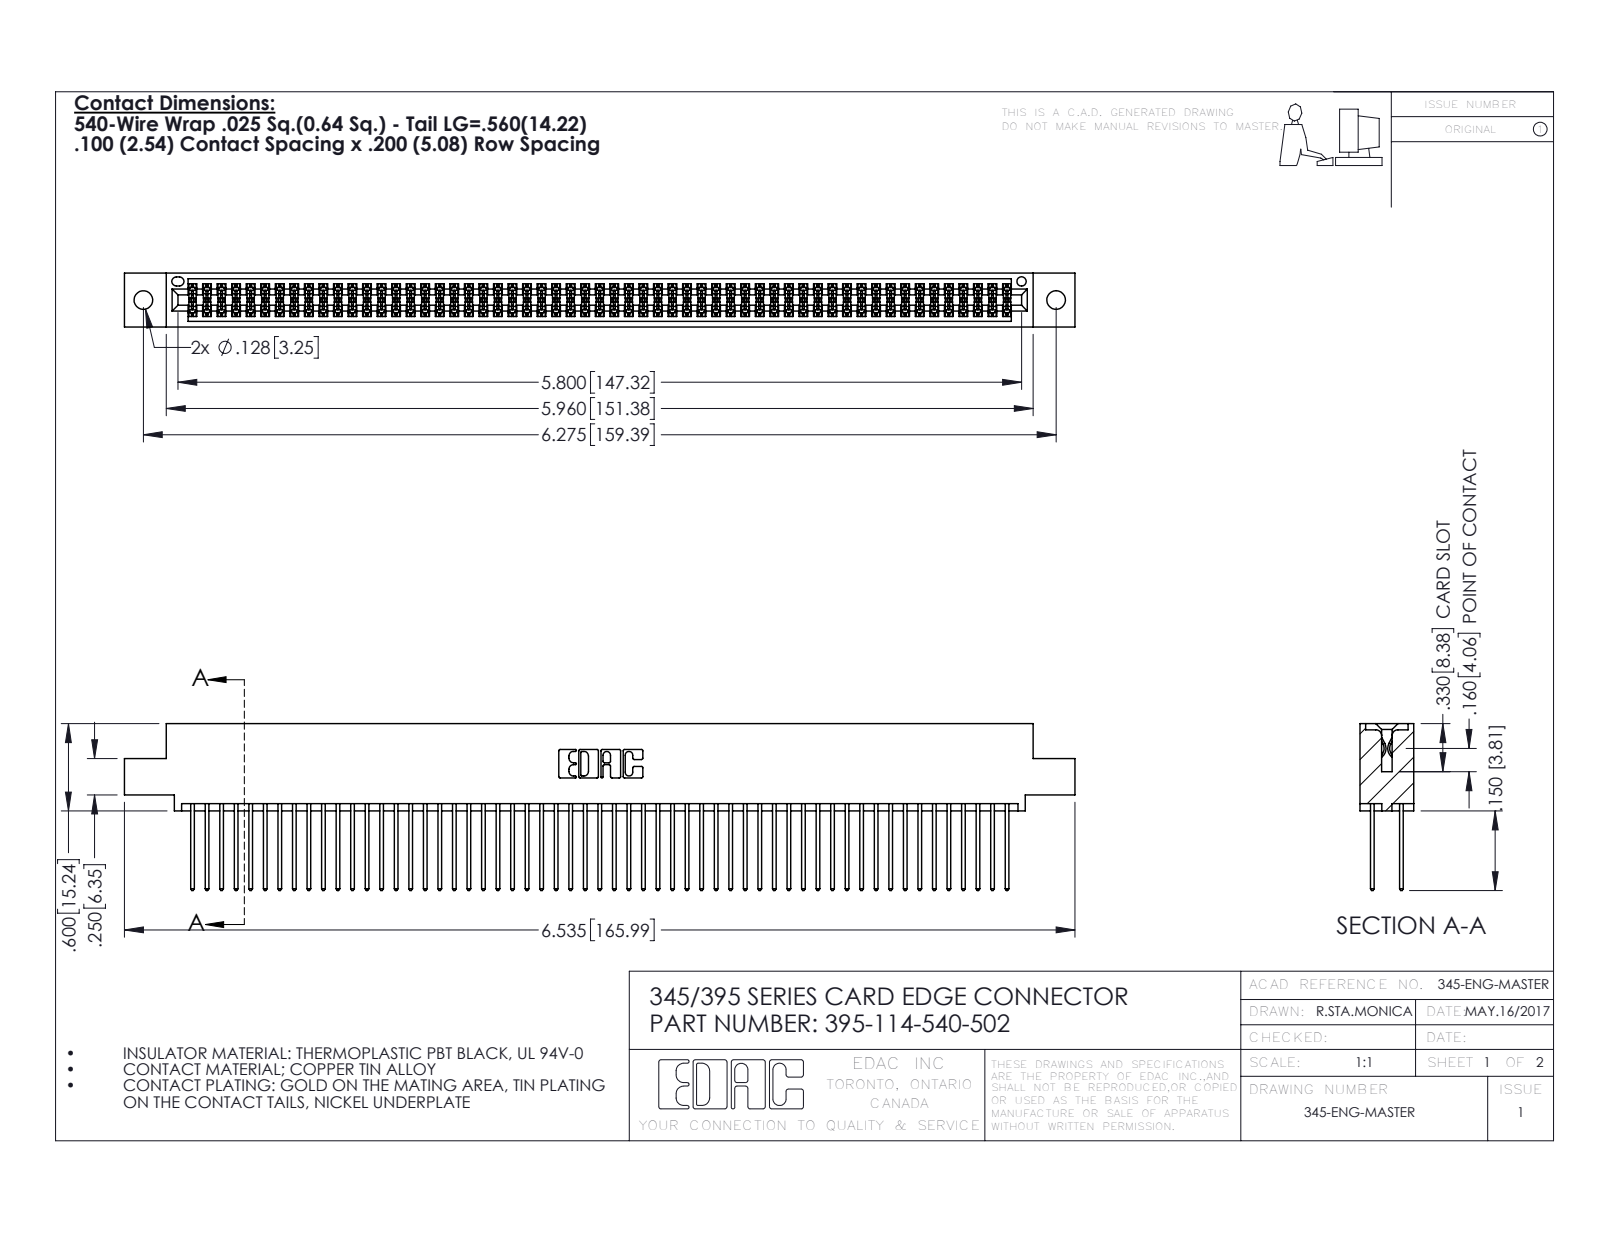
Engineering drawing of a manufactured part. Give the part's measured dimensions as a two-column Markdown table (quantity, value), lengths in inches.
| quantity | value |
| --- | --- |
| part name | 345-292-001_345-293-140; 345 Part_0.110 Offset - 0.128 Dia; 395-114-540-502 |
| STEP written by | SolidWorks 2016 (CONFIG_CONTROL_DESIGN) |
| units | inches |
| bodies | 115 solids, 5830 faces (3846 planar, 1984 cylindrical, 0 other) |
| overall size | 6.535 × 1.147 × 0.37 |
| volume | 1.012 in³ |
| surface area | 41.28 in² |
| round holes (diameter × count) | 0.128 × 2, 0.064 × 1 |
| partial cylindrical surfaces (radius × count) | 0.006 × 171, 0.01 × 114, 0.01 × 22, 0.007 × 6, 0.031 × 6, 0.026 × 3, 0.014 × 2, 0.019 × 2 |
| main face-to-face distances | 0.072, 0.298, 0.2, 0.098, 0.272, 0.025, 0.37, 0.225, 0.175, 0.149 |
| hole center spacings | 0.27, 6.039, 6.275 |
